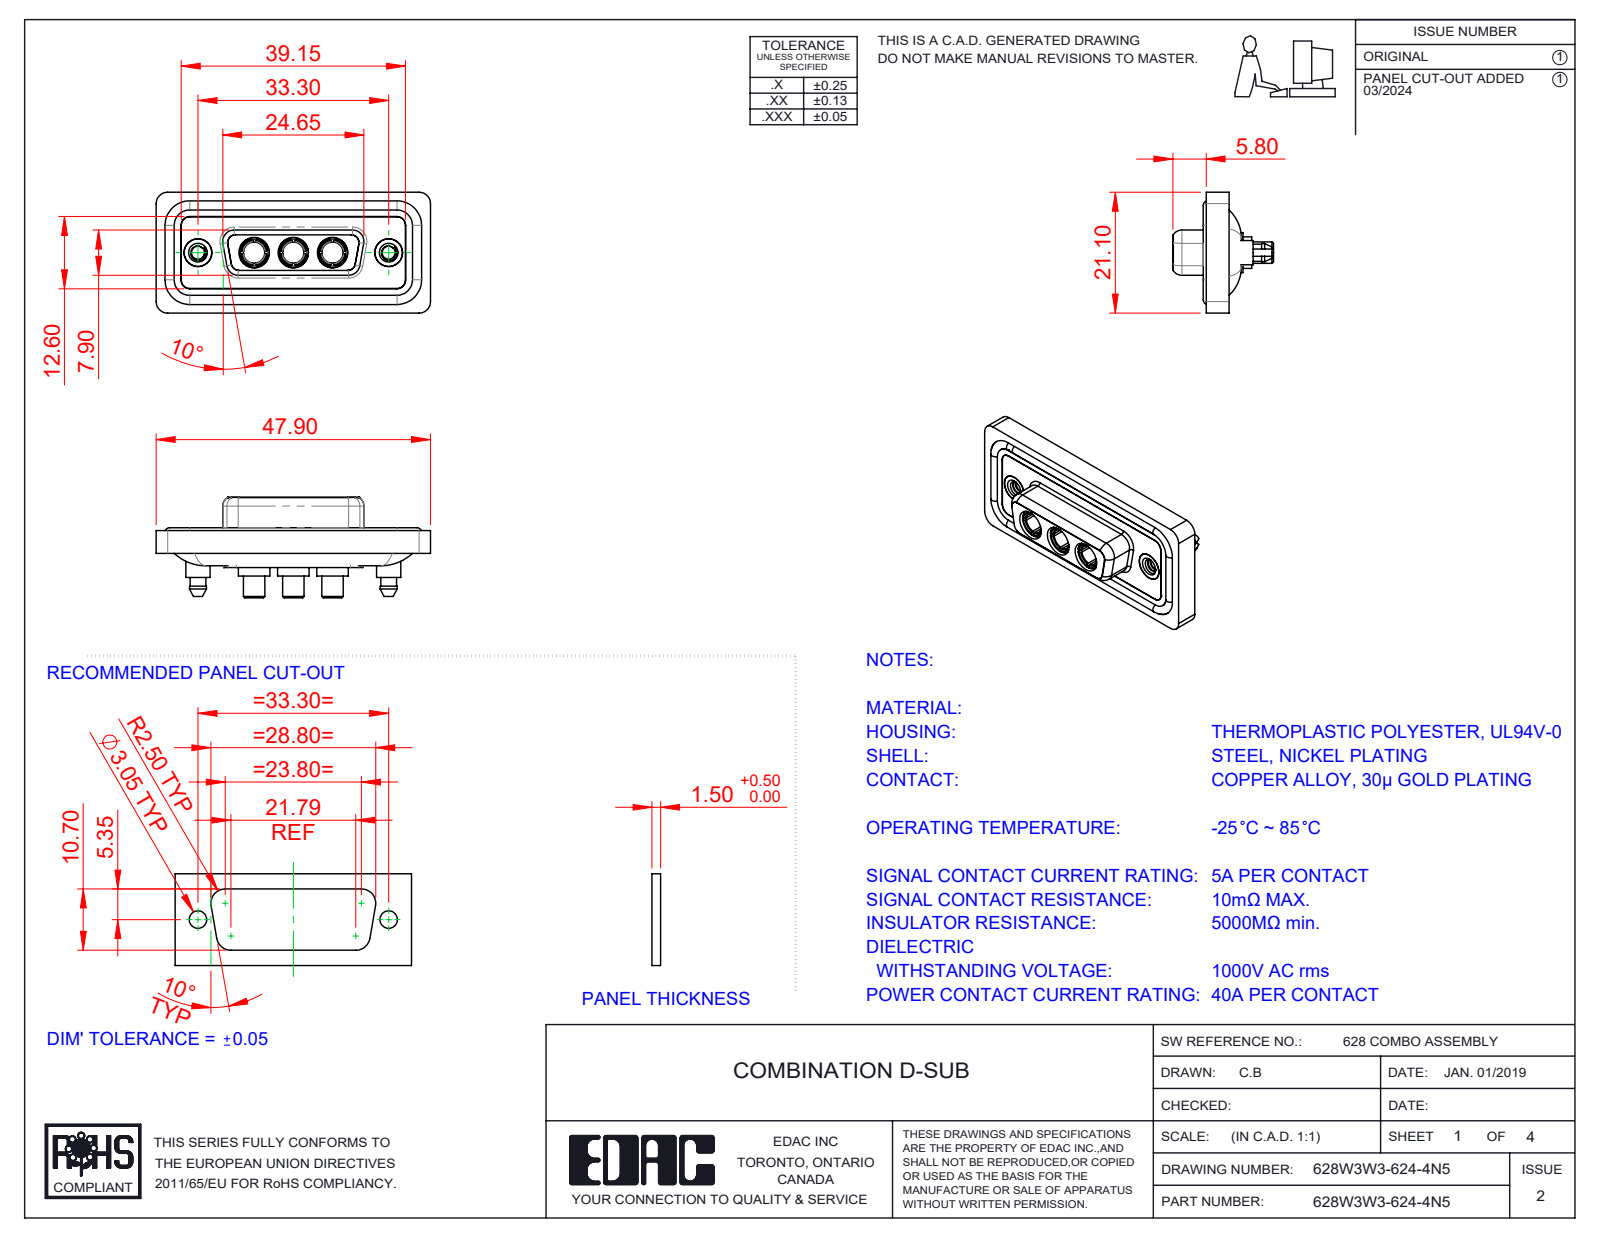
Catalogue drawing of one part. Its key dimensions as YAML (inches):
part_name: "628Combo Waterproof Housing_15 Contacts; Power Socket_40A S; 628Combo Threaded Boardlock_5; 628Combo Housing_3W3 (+3 more)"
step_written_by: "SolidWorks 2023 (CONFIG_CONTROL_DESIGN)"
units: inches
bodies: {solids: 13, faces: 658, planar: 208, cylindrical: 289, other: 161}
overall_size: [1.886, 0.831, 0.691]
volume: 0.379
surface_area: 15.66
round_holes:
  - {diameter: 0.191, count: 5}
  - {diameter: 0.146, count: 3}
  - {diameter: 0.209, count: 3}
  - {diameter: 0.089, count: 2}
  - {diameter: 0.157, count: 2}
  - {diameter: 0.159, count: 2}
  - {diameter: 0.197, count: 2}
round_bosses_or_shafts:
  - {diameter: 0.063, count: 4}
  - {diameter: 0.217, count: 3}
  - {diameter: 0.205, count: 3}
  - {diameter: 0.195, count: 3}
  - {diameter: 0.187, count: 3}
  - {diameter: 0.148, count: 3}
  - {diameter: 0.213, count: 2}
  - {diameter: 0.195, count: 2}
partial_cylinders:
  - {radius: 0.059, count: 24}
  - {radius: 0.079, count: 20}
  - {radius: 0.053, count: 12}
  - {radius: 0.063, count: 10}
  - {radius: 0.01, count: 4}
  - {radius: 0.02, count: 4}
  - {radius: 0.024, count: 4}
  - {radius: 0.026, count: 4}
face_to_face_distances: [0.016, 0.071, 0.063, 0.02, 0.293, 0.043, 0.114, 0.222, 0.278, 0.26]
hole_center_spacings: [0.27, 0.386, 0.656, 0.925, 0.539, 1.311]
